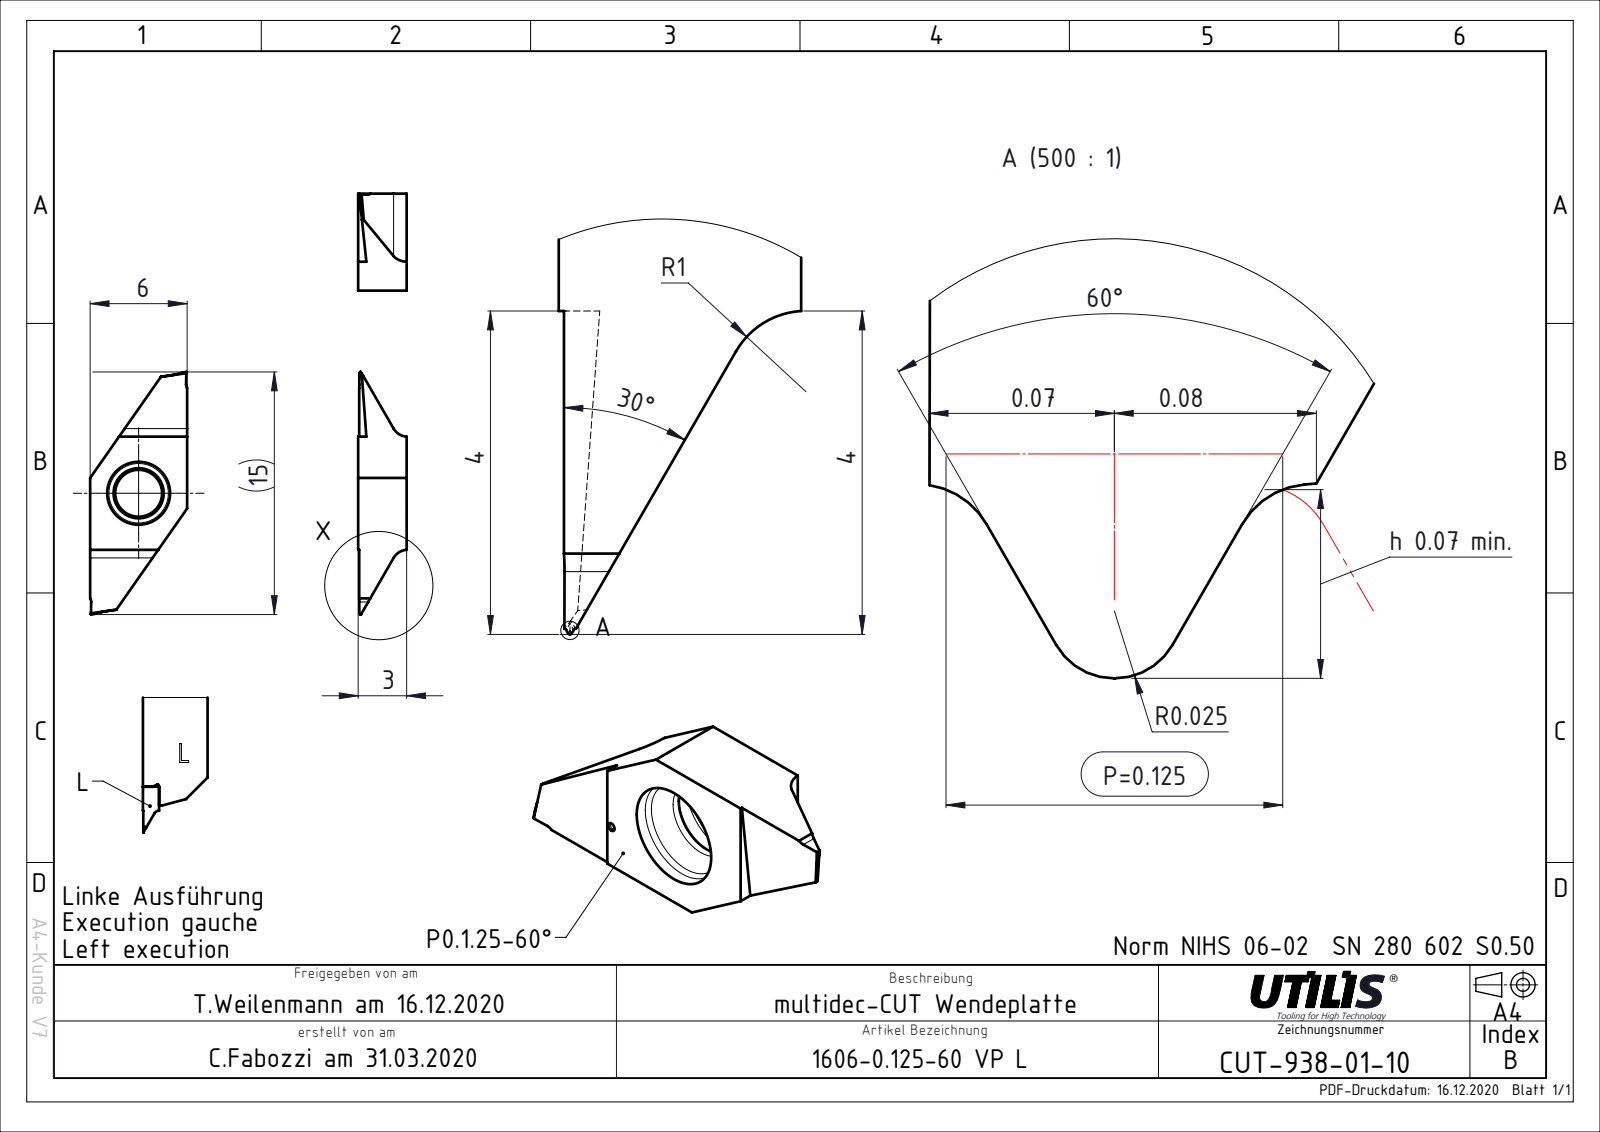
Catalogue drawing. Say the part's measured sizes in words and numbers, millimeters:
The part is named "CUT-938-01; ASME Y14.5". Its 3-D file was written by "FormatWorks Professional (AP242_MANAGED_MODEL_BASED_3D_ENGINEERING_MIM_LF)". It is 1 solid with 34 faces: 20 planar, 14 cylindrical and 0 other. Overall it measures 15 by 6 by 3 millimeters. Its volume is 124 cubic millimeters and its surface area 209 square millimeters. Round holes: 1 of diameter 2.9. Partial cylindrical surfaces (rounded edges, fillets, slot ends): 2 of radius 1. The main face-to-face distances are 6, 3, 9, 7, 12, 7.2.
